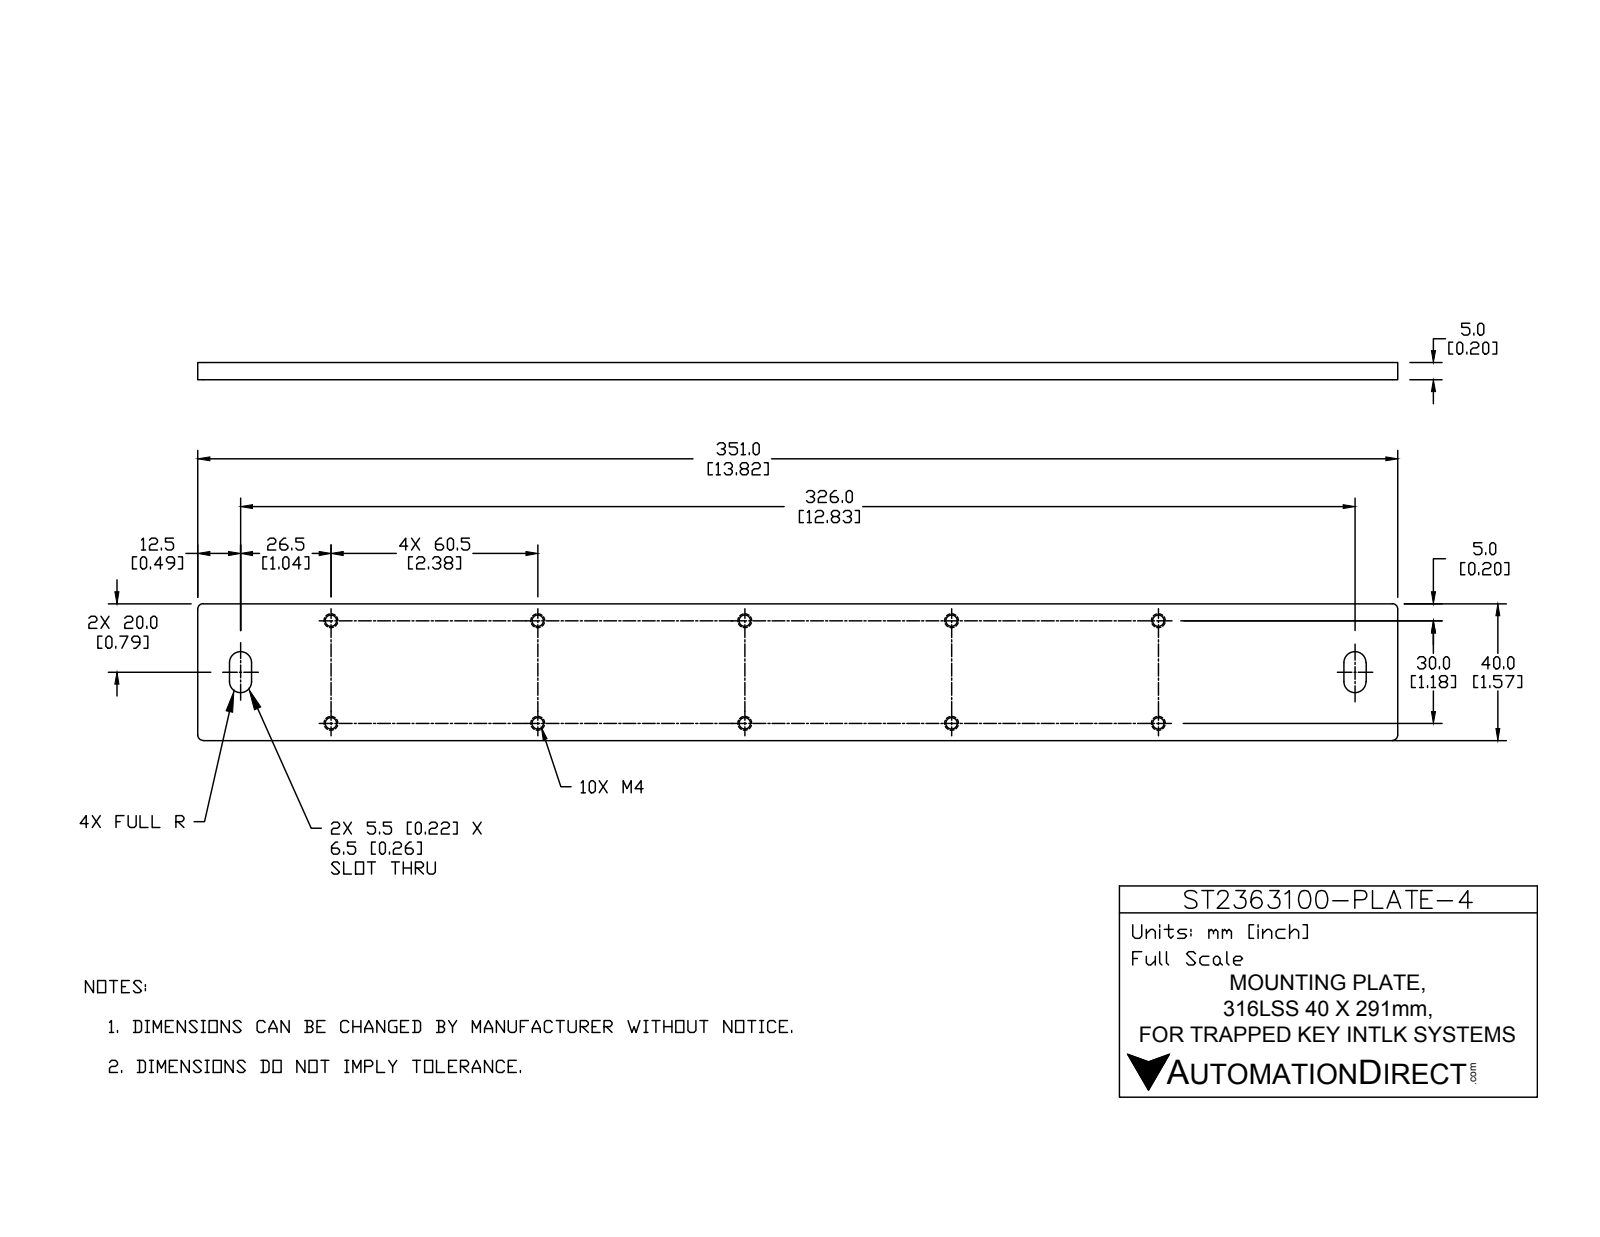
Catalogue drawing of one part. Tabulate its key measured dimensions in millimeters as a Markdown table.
| quantity | value |
| --- | --- |
| part name | ST2363100-PLATE-4 |
| STEP written by | SolidWorks 2017 (AUTOMOTIVE_DESIGN) |
| units | millimeters |
| bodies | 1 solid, 60 faces (10 planar, 34 cylindrical, 16 other) |
| overall size | 351 × 40 × 5 |
| volume | 68 990 mm³ |
| surface area | 32 010 mm² |
| round holes (diameter × count) | 3.3 × 10 |
| partial cylindrical surfaces (radius × count) | 0.2 × 8, 0.5 × 8, 2 × 4, 3.3 × 4 |
| main face-to-face distances | 5, 40, 351, 9.2, 15.7, 335.3, 341.8, 6.5, 326, 332.5 |
| hole center spacings | 60, 67.1, 120, 123.7, 30, 180, 182.5, 240 |
